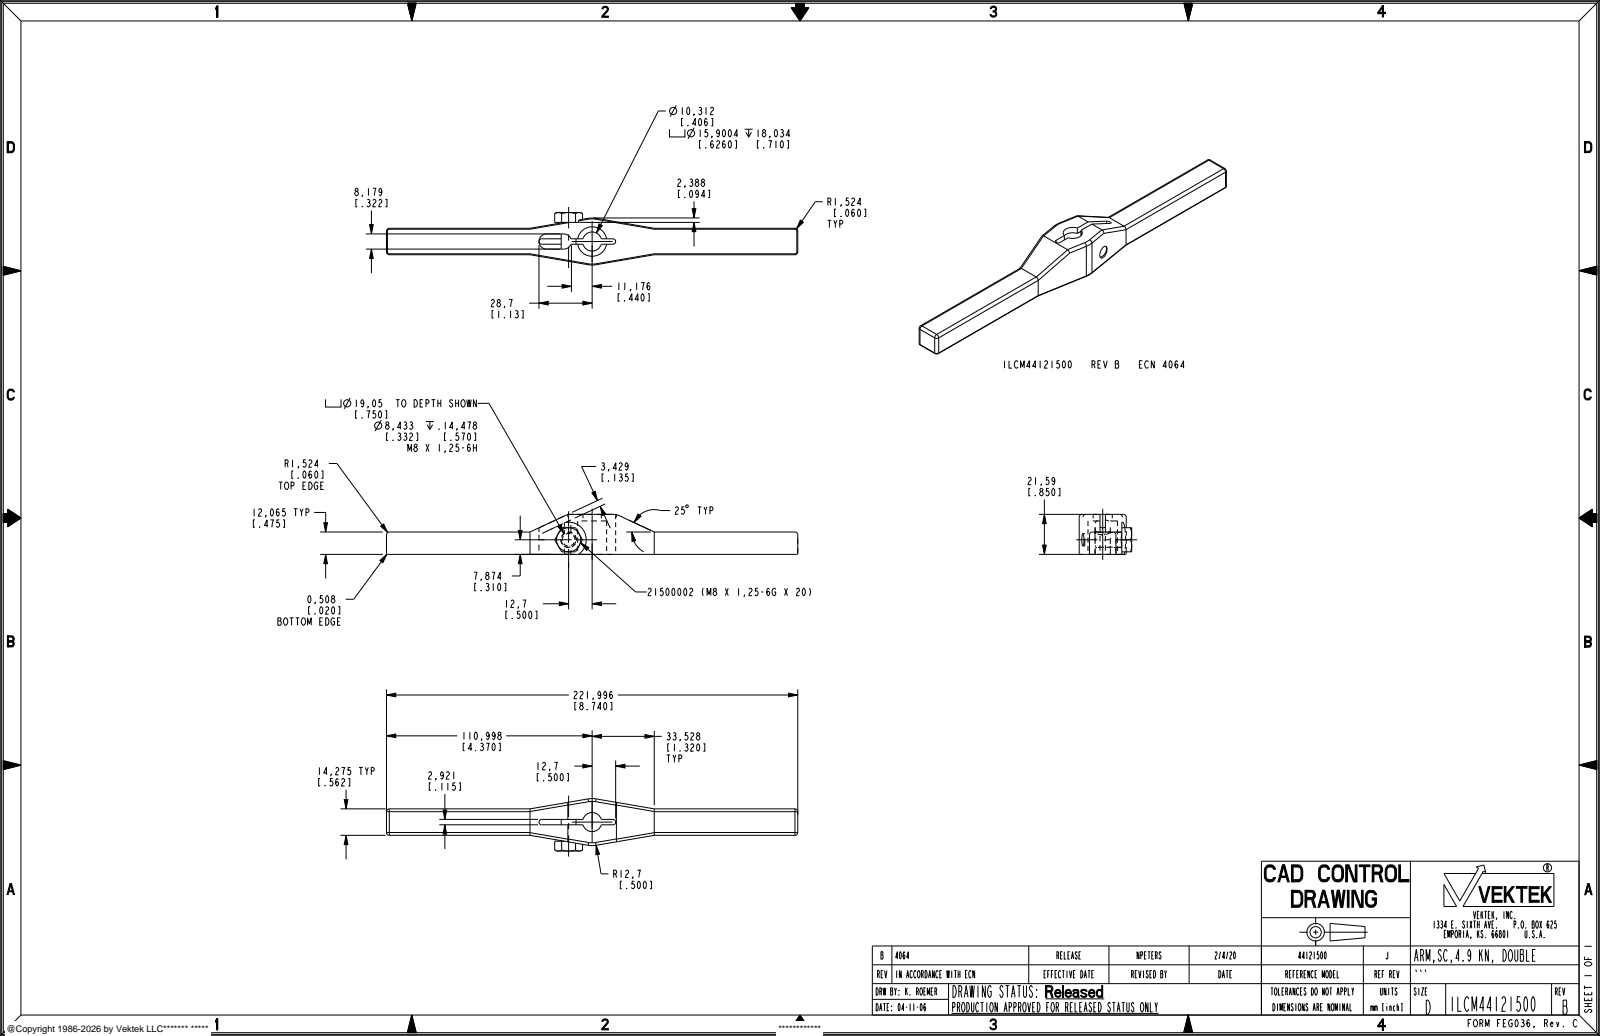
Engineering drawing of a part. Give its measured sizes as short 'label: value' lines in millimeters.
name: ILCM44121500
written by: PRO/ENGINEER BY PARAMETRIC TECHNOLOGY CORPORATION, 2013320 (AUTOMOTIVE_DESIGN)
unit: mm
bodies: 1 solid, 106 faces (37 planar, 51 cylindrical, 18 other)
size: 222 × 28.32 × 21.59
volume: 46 465 mm³; area: 15 914 mm²
holes: 1× ⌀6.78, 1× ⌀8.43, 1× ⌀10.31, 1× ⌀15.9
bosses: 1× ⌀8
rounds: 16× R1.52, 8× R0.51, 2× R1.46, 2× R4.09, 1× R9.53, 1× R12.7
face distances: 12.06, 14.28, 25.4, 5.68, 8.6, 21.59, 9.53, 3.05, 11.23, 2.63
